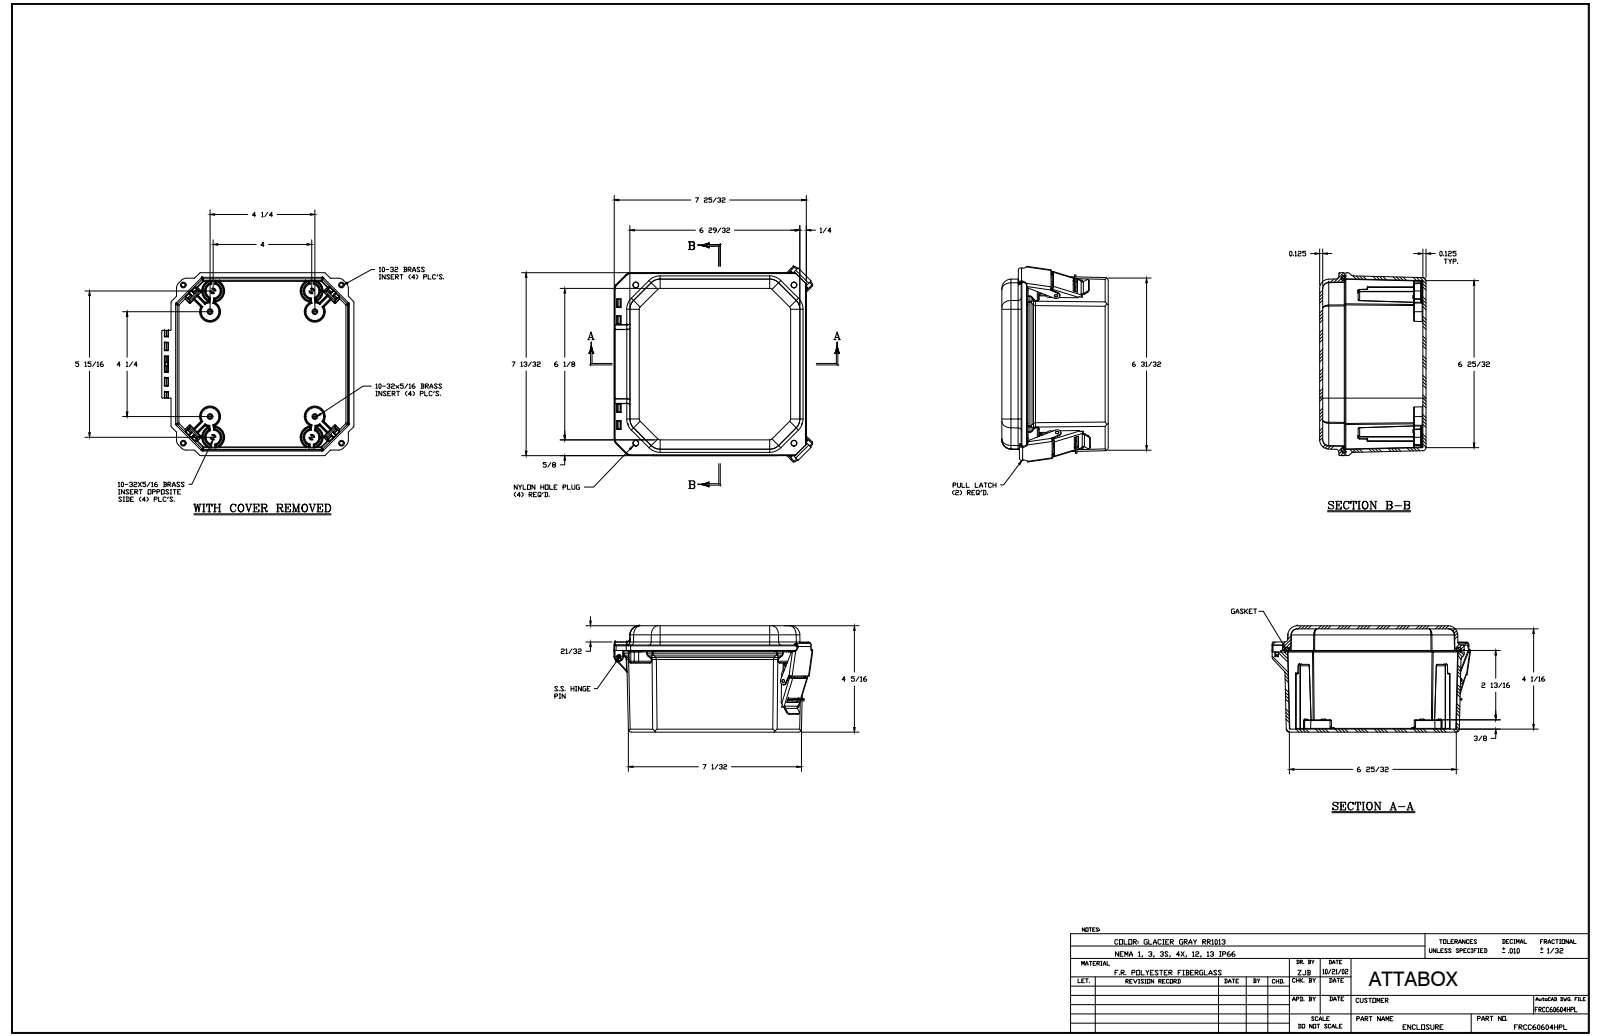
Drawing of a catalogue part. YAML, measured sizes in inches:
part_name: "FRCC60604HPL"
step_written_by: "SolidWorks 2018 (AUTOMOTIVE_DESIGN)"
units: inches
bodies: {solids: 31, faces: 2131, planar: 648, cylindrical: 833, other: 650}
overall_size: [8.108, 8.044, 4.312]
volume: 32.2
surface_area: 507.2
round_holes:
  - {diameter: 0.156, count: 12}
  - {diameter: 0.152, count: 8}
  - {diameter: 0.135, count: 6}
  - {diameter: 0.135, count: 4}
  - {diameter: 0.15, count: 4}
  - {diameter: 0.219, count: 4}
  - {diameter: 0.252, count: 4}
  - {diameter: 0.312, count: 4}
  - {diameter: 0.137, count: 1}
  - {diameter: 0.375, count: 1}
  - {diameter: 0.375, count: 1}
round_bosses_or_shafts:
  - {diameter: 0.246, count: 12}
  - {diameter: 0.87, count: 4}
  - {diameter: 0.209, count: 4}
  - {diameter: 0.3, count: 2}
  - {diameter: 0.135, count: 1}
  - {diameter: 0.135, count: 1}
partial_cylinders:
  - {radius: 0.01, count: 136}
  - {radius: 0.005, count: 96}
  - {radius: 0.02, count: 65}
  - {radius: 0.03, count: 58}
  - {radius: 0.125, count: 29}
  - {radius: 0.09, count: 26}
  - {radius: 0.03, count: 24}
  - {radius: 0.06, count: 24}
face_to_face_distances: [0.125, 4.187, 4.062, 4.312, 0.124, 0.125, 0.05, 0.656, 3.531, 1]
hole_center_spacings: [5.441, 6.414, 6.289, 4.25, 5.091, 7.541, 0.25, 0.849]
